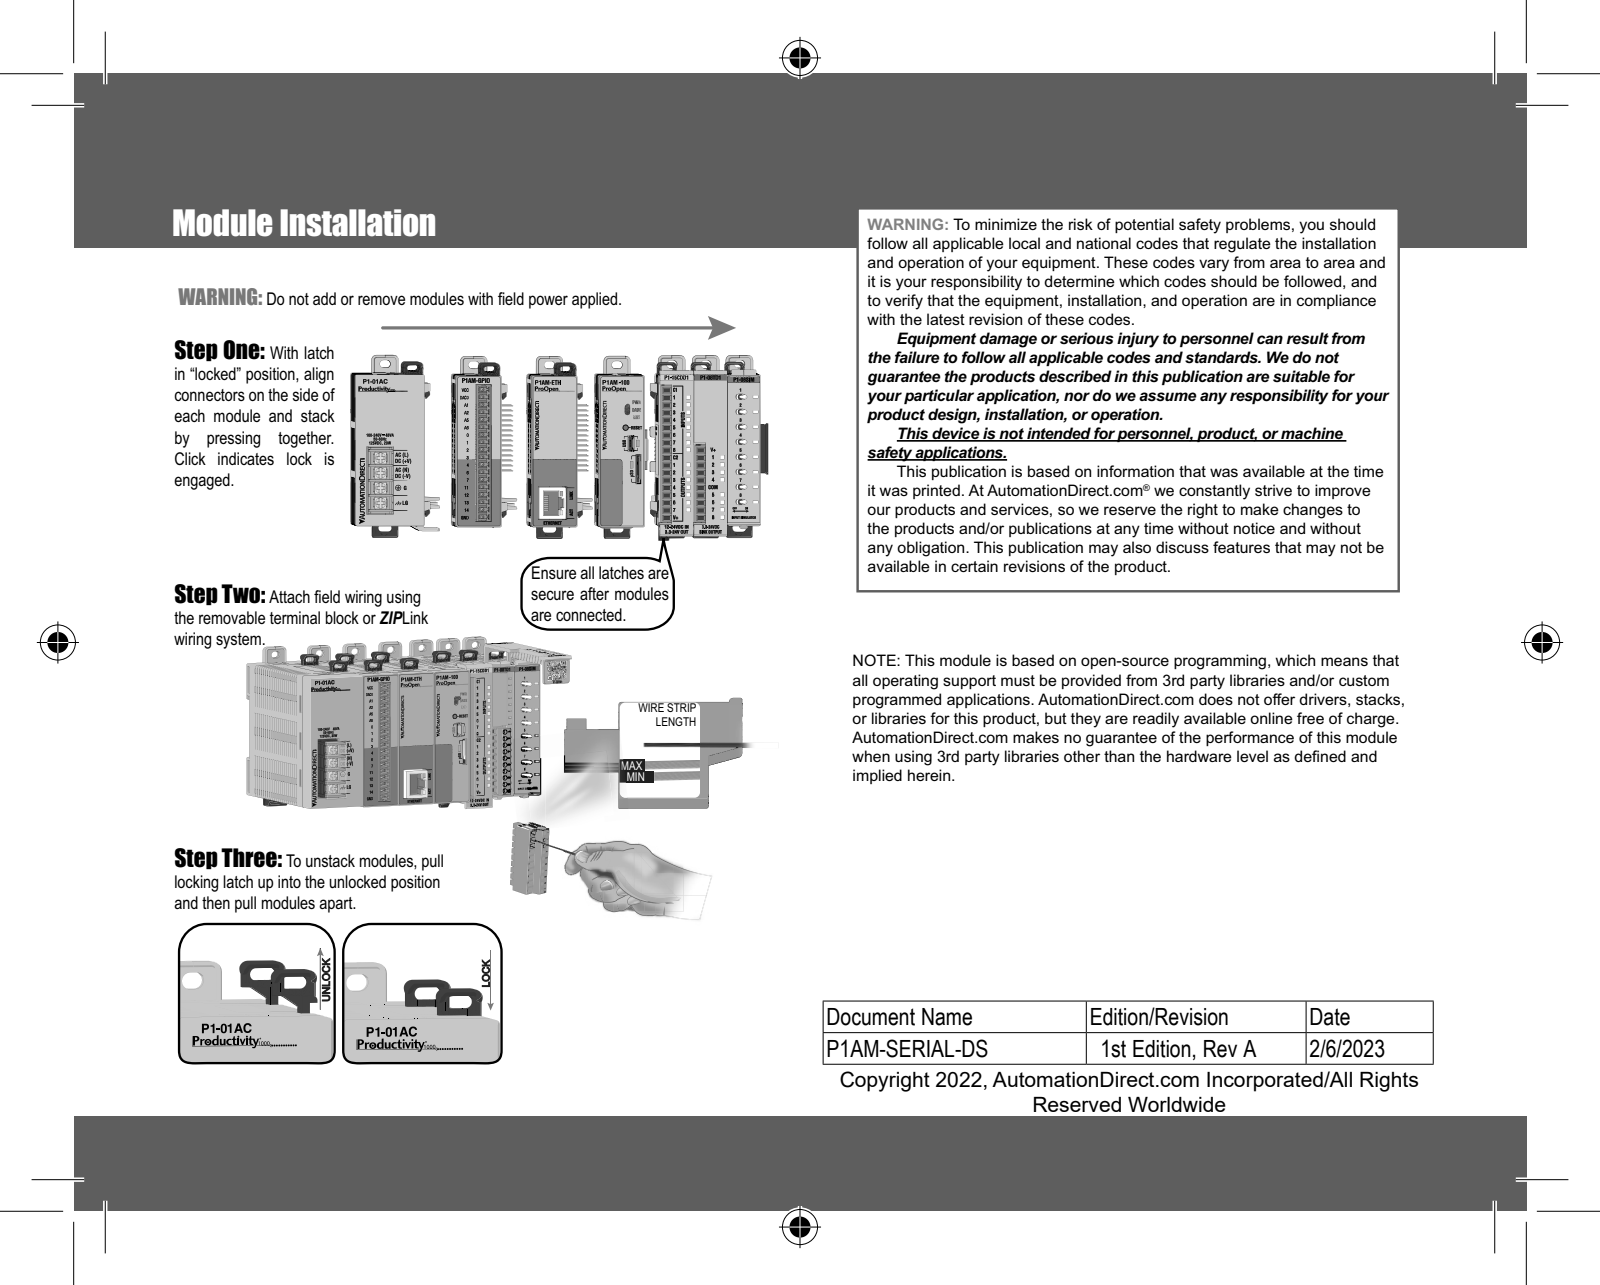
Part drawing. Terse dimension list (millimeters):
name: P1AM-SERIAL nc red1 ext1ccB DIN Coord fxtt
written by: SolidWorks 2021 (AUTOMOTIVE_DESIGN)
unit: mm
bodies: 6 solids, 3263 faces (1795 planar, 805 cylindrical, 663 other)
size: 100.6 × 92.8 × 31.9
volume: 157 100 mm³; area: 30 790 mm²
holes: 33× ⌀0.3, 8× ⌀2, 8× ⌀2.8
rounds: 160× R0.3, 99× R0.5, 49× R1, 44× R0.2, 13× R2, 10× R1.5, 8× R1.8, 6× R1.2
face distances: 23.2, 77, 23.2, 82.7, 23.1, 3.8, 86.4, 19.6, 19.6, 3.5
hole spacings: 2.5, 3.5, 5.1, 20.4, 7.6, 20.8, 10.2, 21.6
